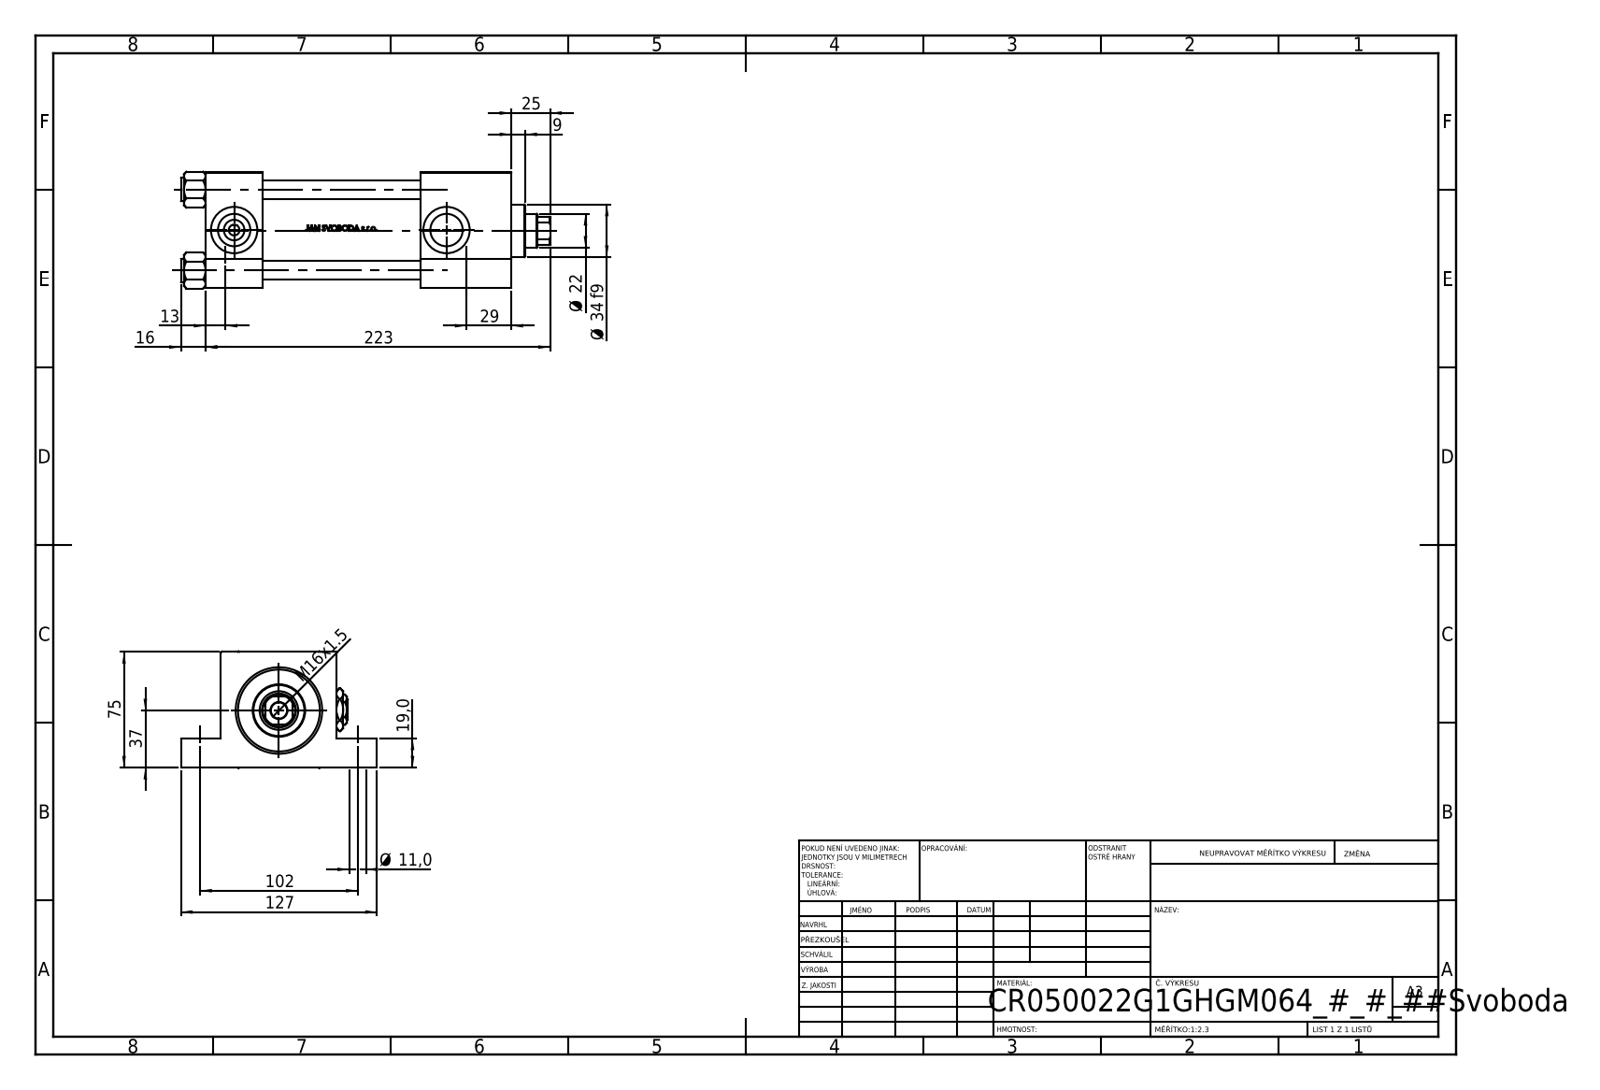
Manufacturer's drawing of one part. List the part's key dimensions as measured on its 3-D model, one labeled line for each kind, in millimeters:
Part name (STEP PRODUCT): V215CR_G_TYCINKA; V215_VC_A; V215CR_G_Body; V215CR_VCP_G (+2 more)
STEP written by: SolidWorks 2019 (CONFIG_CONTROL_DESIGN)
Units: millimetres
Bodies: 12 solids, 1134 faces (454 planar, 128 cylindrical, 552 other)
Overall size (bounding box): 239 × 127 × 75.54
Volume: 811 013 mm³ · Surface area: 185 632 mm²
Round holes (diameter × count): ⌀11 ×4, ⌀12 ×4, ⌀7 ×2, ⌀20.96 ×2, ⌀30 ×2, ⌀10.5 ×1, ⌀22 ×1, ⌀25 ×1, ⌀41 ×1, ⌀50 ×1, ⌀53 ×1
Round bosses / shafts (diameter × count): ⌀15 ×4, ⌀56 ×1, ⌀34 ×1
Partial cylindrical surfaces — rounded edges, fillets, slot ends (radius × count): R10.5 ×1
Main face-to-face distances: 75, 37, 198, 161, 19, 56, 139, 102, 59, 26
Hole centre spacings: 52.3, 36.63, 37.34, 73.96, 102, 156, 186.39, 137.5
